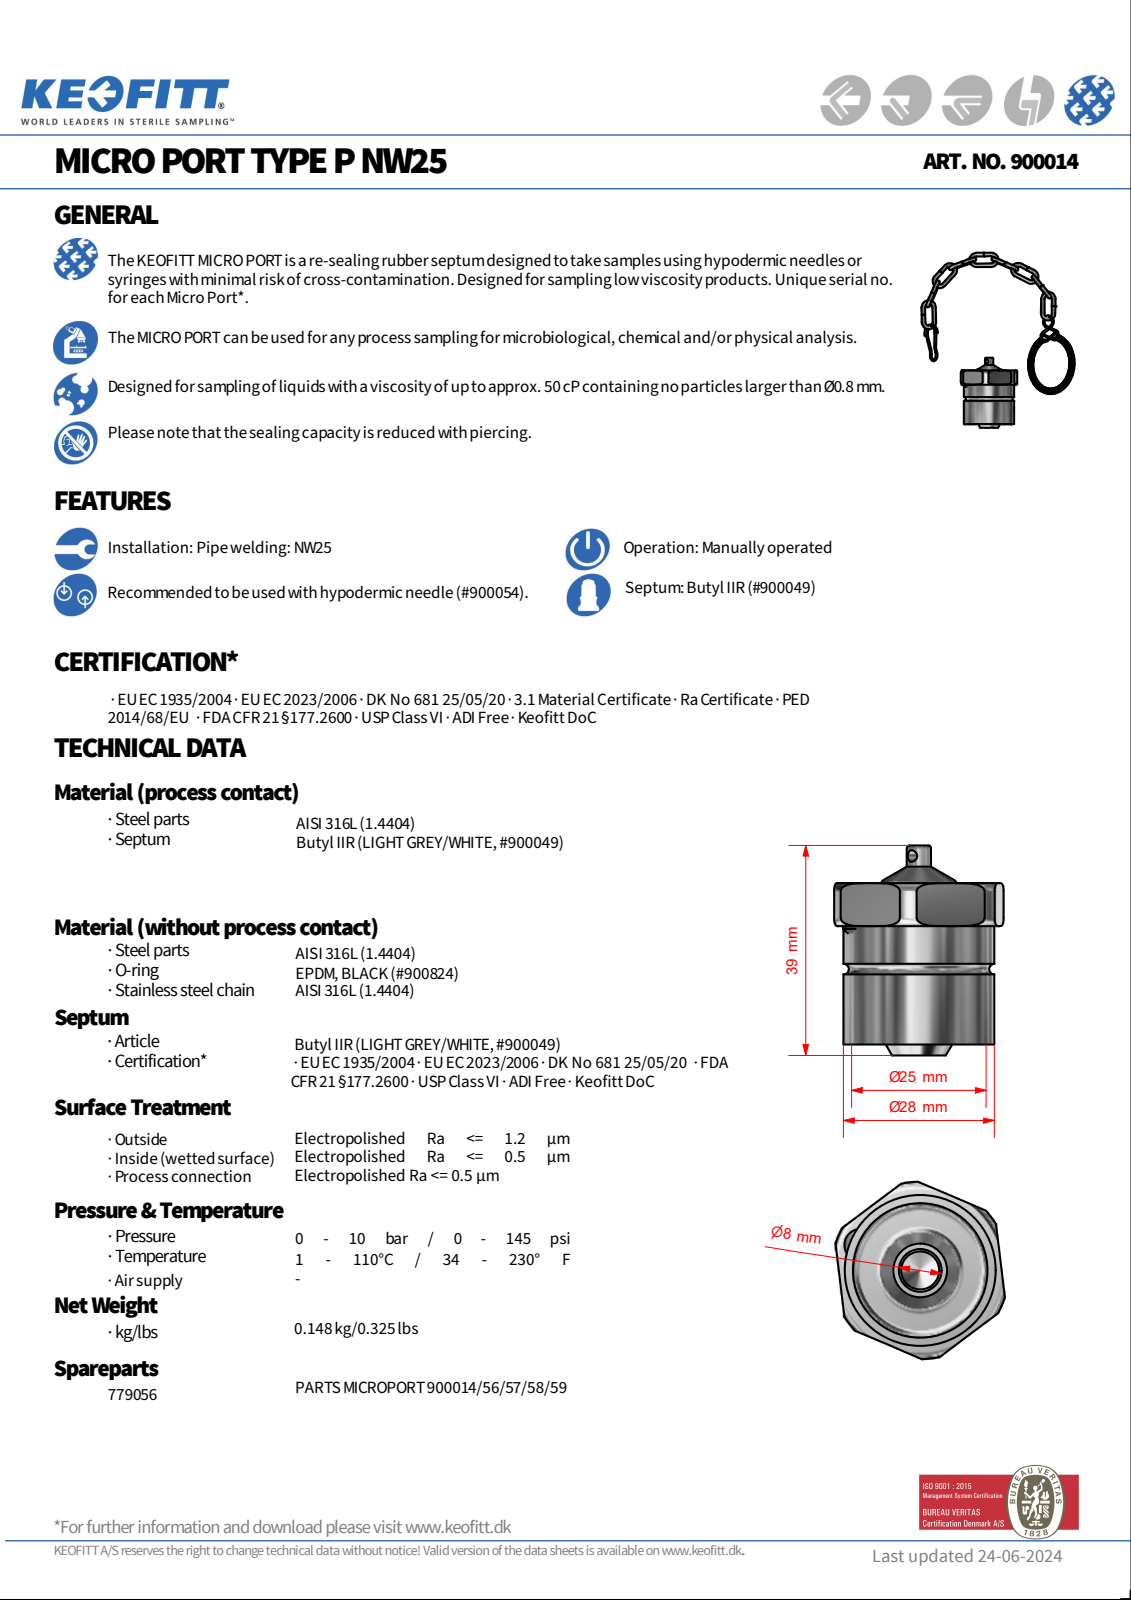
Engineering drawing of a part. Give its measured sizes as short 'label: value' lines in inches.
written by: Autodesk Inventor 2008 (AUTOMOTIVE_DESIGN)
unit: in
bodies: 18 solids, 372 faces (65 planar, 71 cylindrical, 236 other)
size: 3.786 × 3.089 × 2.074
volume: 1.271 in³; area: 14.12 in²
holes: 9× ⌀0.079, 1× ⌀0.008, 1× ⌀0.087, 1× ⌀0.205, 1× ⌀0.984
bosses: 21× ⌀0.079, 1× ⌀1.102, 1× ⌀0.551, 1× ⌀0.433, 1× ⌀0.276, 1× ⌀0.177
rounds: 8× R0.004, 1× R0.118, 1× R0.471, 1× R0.65
face distances: 1.181, 1.102, 0.079, 1.182, 0.315, 0.787, 0.866, 0.049, 0.266, 1.054
hole spacings: 0.118, 0.472
